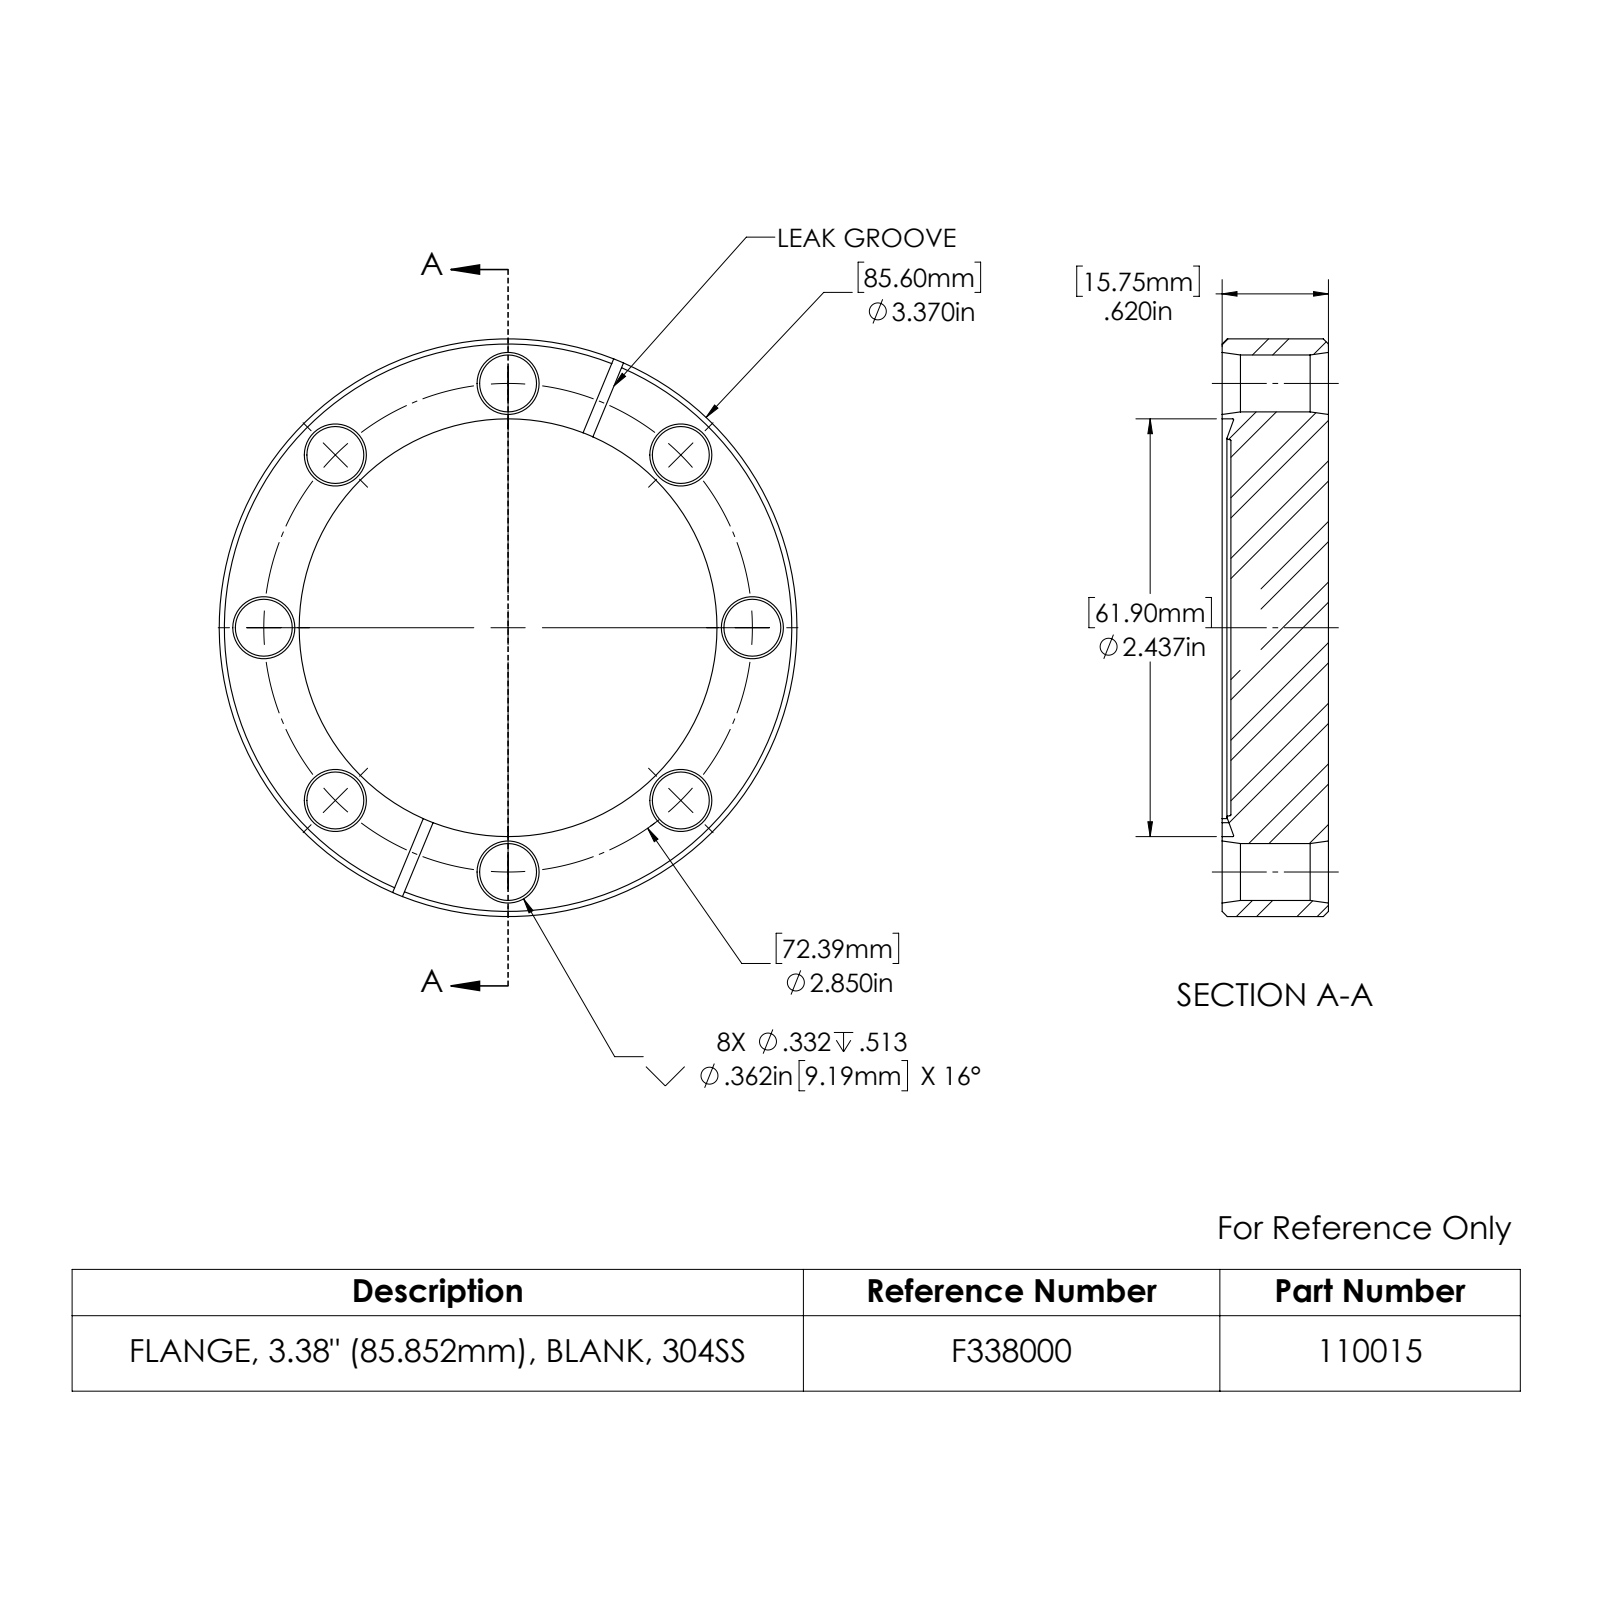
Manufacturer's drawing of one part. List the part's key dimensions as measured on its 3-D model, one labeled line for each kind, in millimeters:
Part name (STEP PRODUCT): 110015
STEP written by: SolidWorks 2022 (AUTOMOTIVE_DESIGN)
Units: millimetres
Bodies: 1 solid, 77 faces (10 planar, 20 cylindrical, 47 other)
Overall size (bounding box): 85.6 × 85.6 × 15.7
Volume: 79 310 mm³ · Surface area: 18 320 mm²
Round holes (diameter × count): ⌀8.4 ×8, ⌀61.9 ×1
Round bosses / shafts (diameter × count): ⌀85.6 ×1
Main face-to-face distances: 14.5, 1.3, 15.7, 1.3, 14.4, 1.6, 1.5, 1.6
Hole centre spacings: 27.7, 66.9, 36.2, 36.2, 51.2, 51.2, 72.4, 72.4
